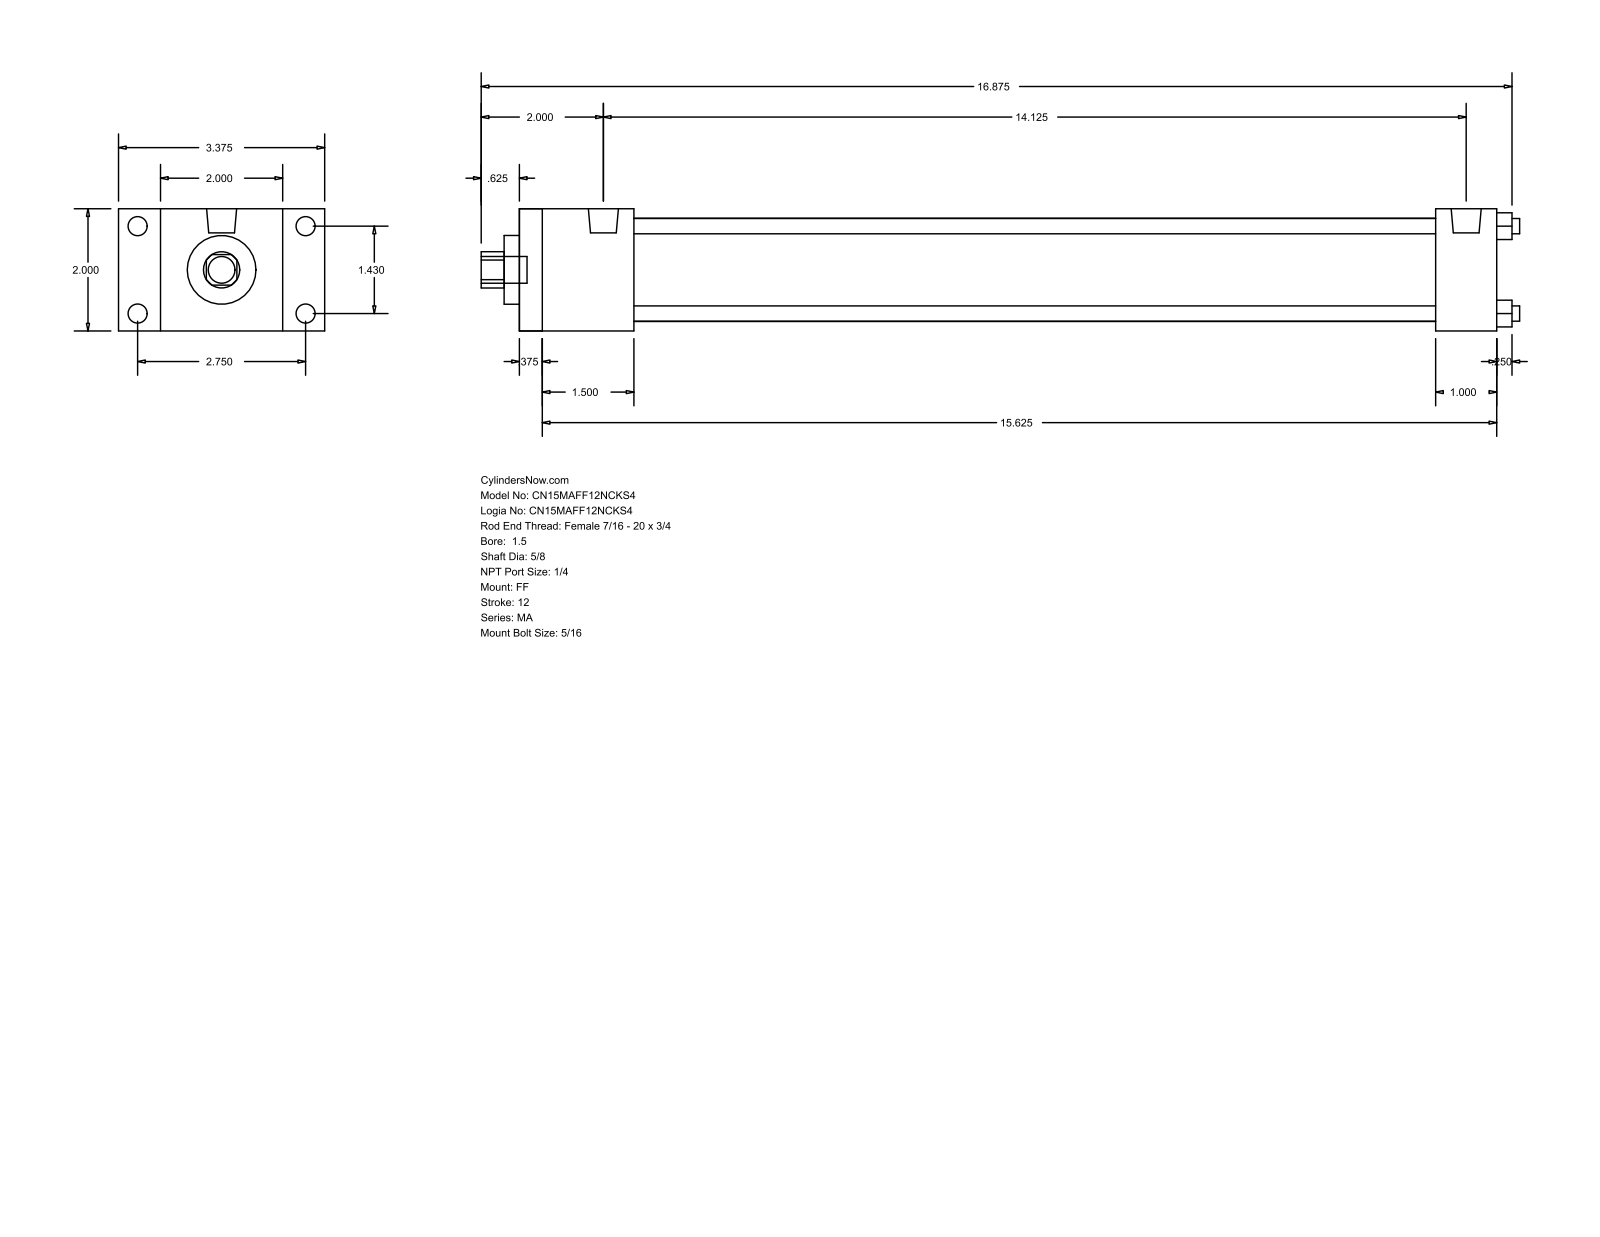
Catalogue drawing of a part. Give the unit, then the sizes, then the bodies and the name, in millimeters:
Units: millimetres
Overall size (bounding box): 431.8 × 85.72 × 50.8
Round holes (diameter × count): ⌀6.35 ×4, ⌀15.88 ×1, ⌀28.57 ×1, ⌀42.93 ×1
Round bosses / shafts (diameter × count): ⌀7.94 ×8, ⌀12.49 ×2, ⌀11.11 ×1
Partial cylindrical surfaces — rounded edges, fillets, slot ends (radius × count): R7.54 ×1
Main face-to-face distances: 50.8, 406.39, 9.52, 396.87, 47.62, 381, 38.1, 371.48, 333.38, 358.77
Hole centre spacings: 25.68, 36.32, 51.36
Bodies: 0 solids, 92 faces (64 planar, 28 cylindrical, 0 other)
Part name (STEP PRODUCT): MA_FF__0150_0.625
STEP written by: GSSL Pune (CONFIG_CONTROL_DESIGN)
